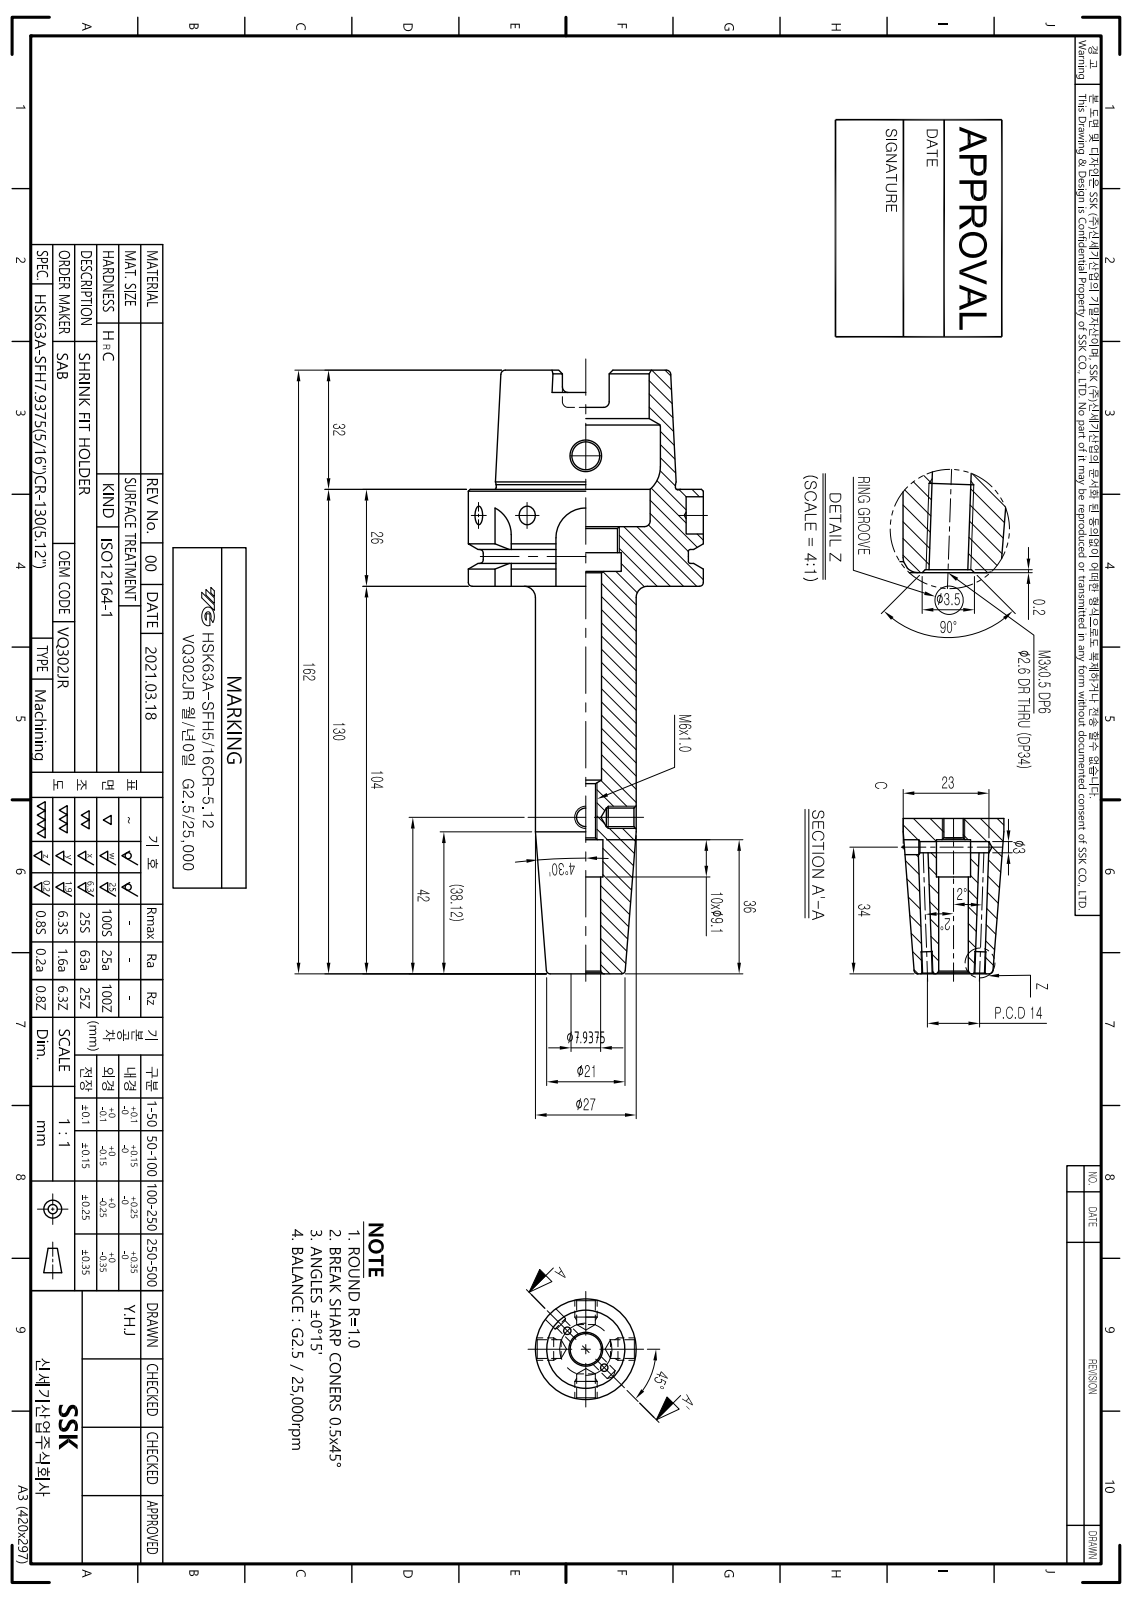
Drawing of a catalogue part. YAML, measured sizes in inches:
part_name: "LO-HSK63A-SFH7.9375CR-130"
step_written_by: "Autodesk Inventor 2022 (AUTOMOTIVE_DESIGN)"
units: inches
bodies: {solids: 1, faces: 121, planar: 42, cylindrical: 36, other: 43}
overall_size: [6.378, 2.48, 2.48]
volume: 8.006
surface_area: 52.01
round_holes:
  - {diameter: 0.097, count: 2}
  - {diameter: 0.194, count: 1}
  - {diameter: 0.295, count: 1}
  - {diameter: 0.313, count: 1}
  - {diameter: 0.331, count: 1}
  - {diameter: 0.358, count: 1}
  - {diameter: 0.394, count: 1}
  - {diameter: 0.666, count: 1}
  - {diameter: 0.748, count: 1}
  - {diameter: 1.339, count: 1}
  - {diameter: 1.575, count: 1}
round_bosses_or_shafts:
  - {diameter: 2.48, count: 1}
  - {diameter: 2.165, count: 1}
  - {diameter: 1.891, count: 1}
  - {diameter: 1.063, count: 1}
partial_cylinders:
  - {radius: 0.059, count: 6}
  - {radius: 0.113, count: 4}
  - {radius: 0.315, count: 4}
face_to_face_distances: [1.024, 0.394, 0.63, 1.26, 1.654, 2.283, 2.087, 0.866, 0.157, 0.472]
